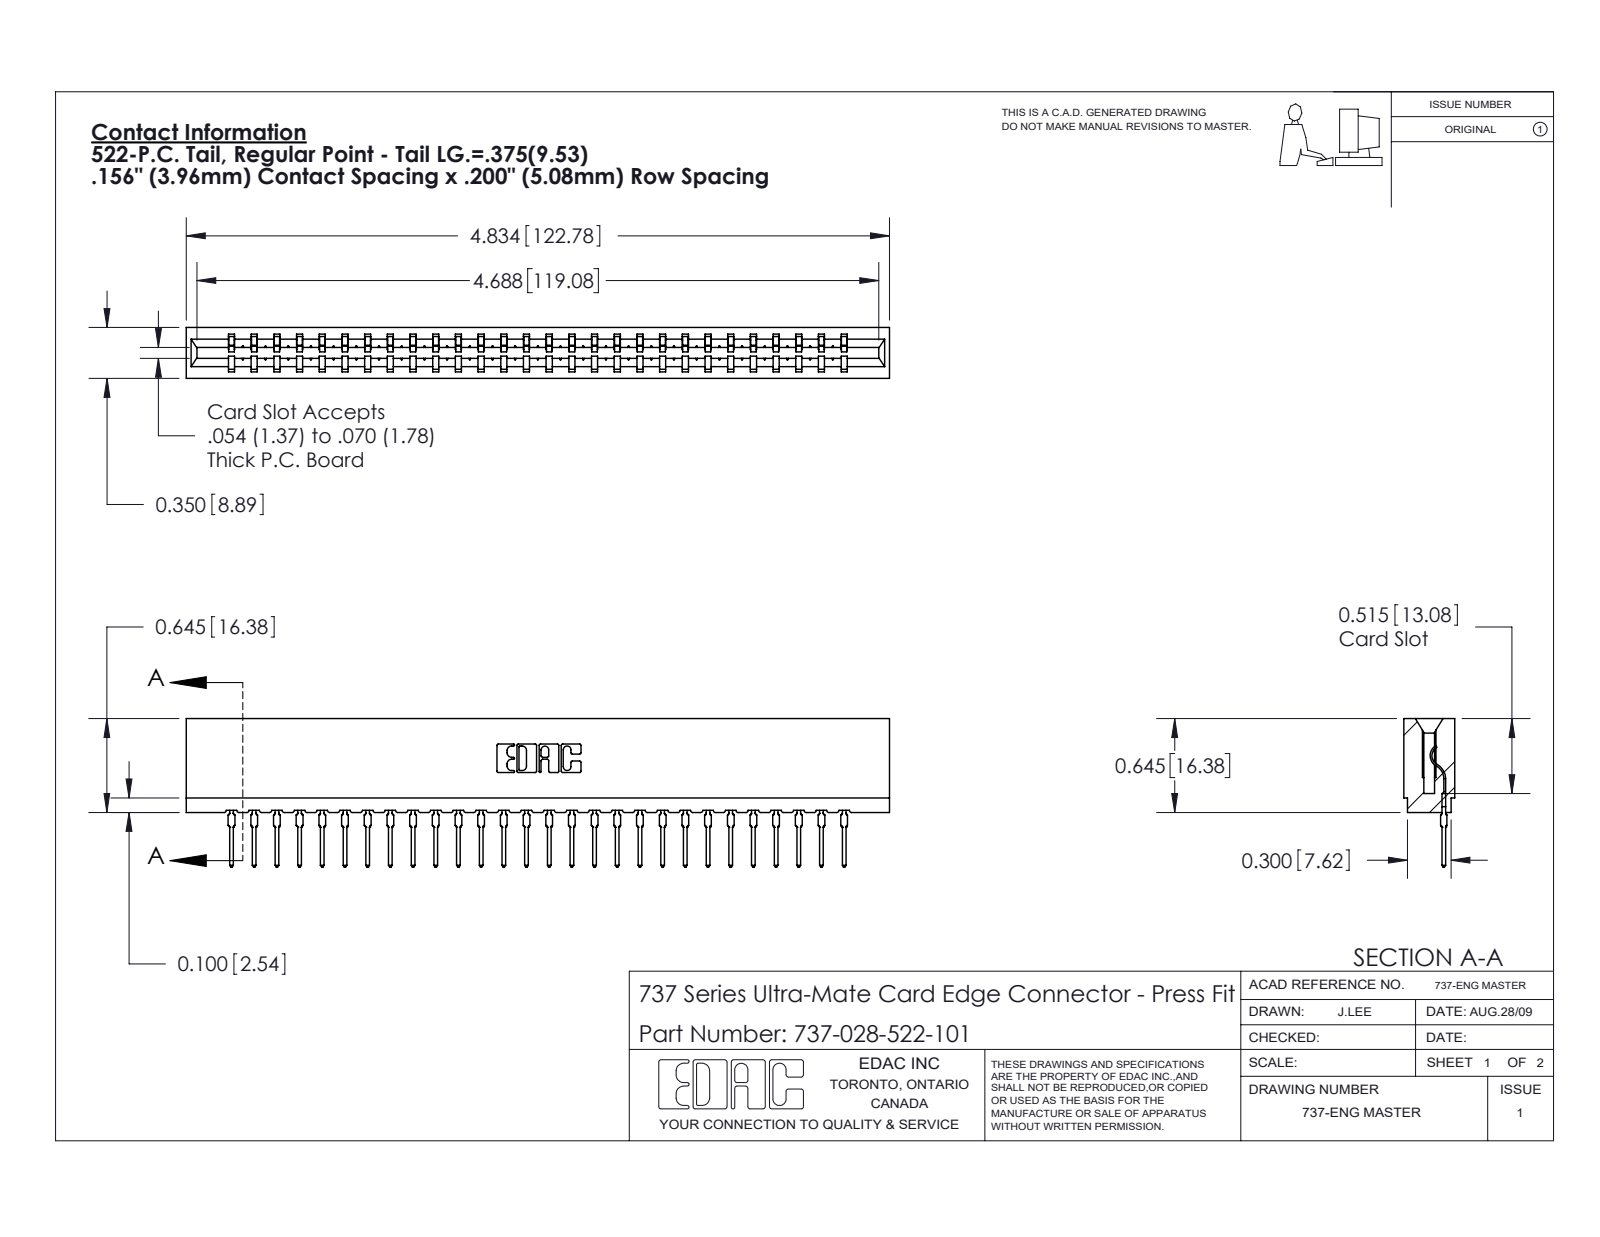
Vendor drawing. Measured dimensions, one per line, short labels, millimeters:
name: 745-292-001_522; 737 Part_Insulator Option - 01; 737-028-522-101
written by: SolidWorks 2020 (CONFIG_CONTROL_DESIGN)
unit: mm
bodies: 29 solids, 3258 faces (1958 planar, 572 cylindrical, 728 other)
size: 122.8 × 25.9 × 8.9
volume: 12 000 mm³; area: 15 910 mm²
rounds: 56× R0.4, 56× R0.5, 22× R0.3, 6× R0.2, 6× R0.8, 4× R0.1, 4× R0.3, 3× R0.7
face distances: 3.5, 5.4, 8.9, 1.9, 15.8, 1.1, 7.7, 2.4, 4.2, 4
